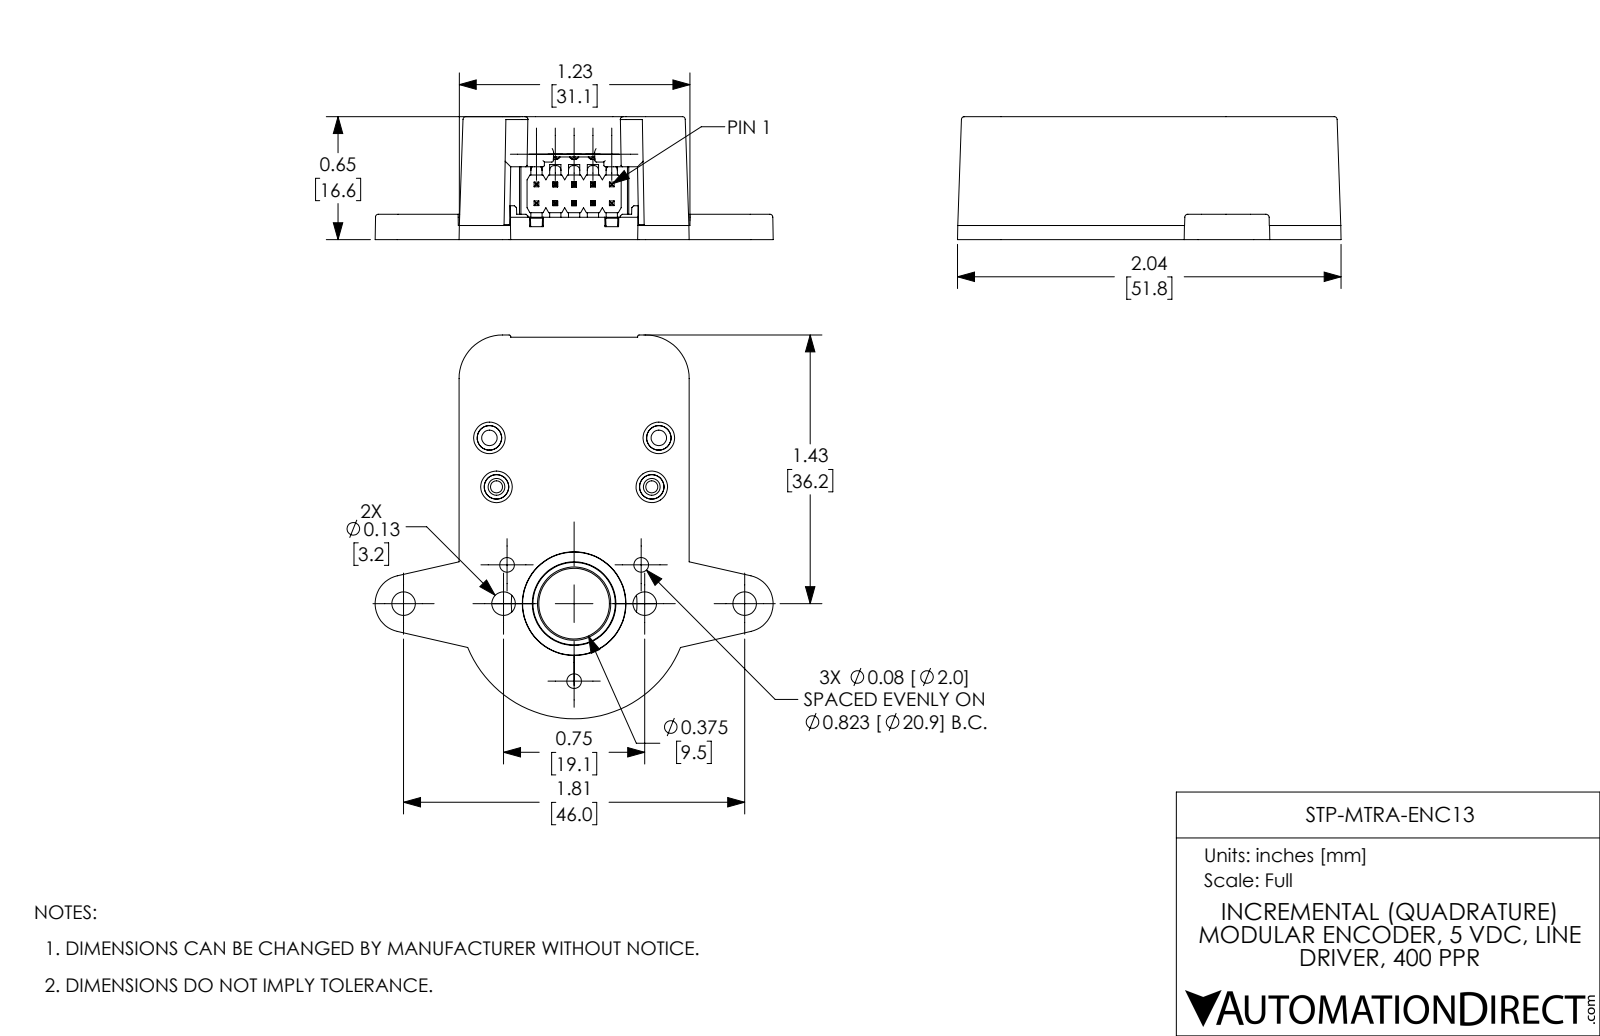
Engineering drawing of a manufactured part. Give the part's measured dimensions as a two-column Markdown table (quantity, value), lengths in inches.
| quantity | value |
| --- | --- |
| part name | STP-MTRA-ENC2 MOD FOR ENC10 12 B1 |
| STEP written by | SolidWorks 2017 (AUTOMOTIVE_DESIGN) |
| units | inches |
| bodies | 13 solids, 1132 faces (410 planar, 288 cylindrical, 434 other) |
| overall size | 2.115 × 1.856 × 0.653 |
| volume | 0.2 in³ |
| surface area | 19.91 in² |
| round holes (diameter × count) | 0.089 × 4, 0.125 × 4, 0.078 × 3, 0.145 × 3, 0.095 × 2, 0.109 × 2, 0.093 × 1, 0.145 × 1, 0.375 × 1, 0.551 × 1 |
| round bosses / shafts (diameter × count) | 0.187 × 4, 0.16 × 4, 0.112 × 3, 0.195 × 2, 0.52 × 1, 0.487 × 1, 0.096 × 1 |
| partial cylindrical surfaces (radius × count) | 0.016 × 36, 0.031 × 24, 0.01 × 4, 0.047 × 2, 0.047 × 2, 0.048 × 2, 0.075 × 2, 0.095 × 2 |
| main face-to-face distances | 0.653, 0.135, 0.518, 0.405, 0.54, 0.113, 0.398, 0.458, 1.1, 0.533 |
| hole center spacings | 0.162, 0.207, 0.282, 0.411, 0.418, 0.531, 0.557, 0.587 |
